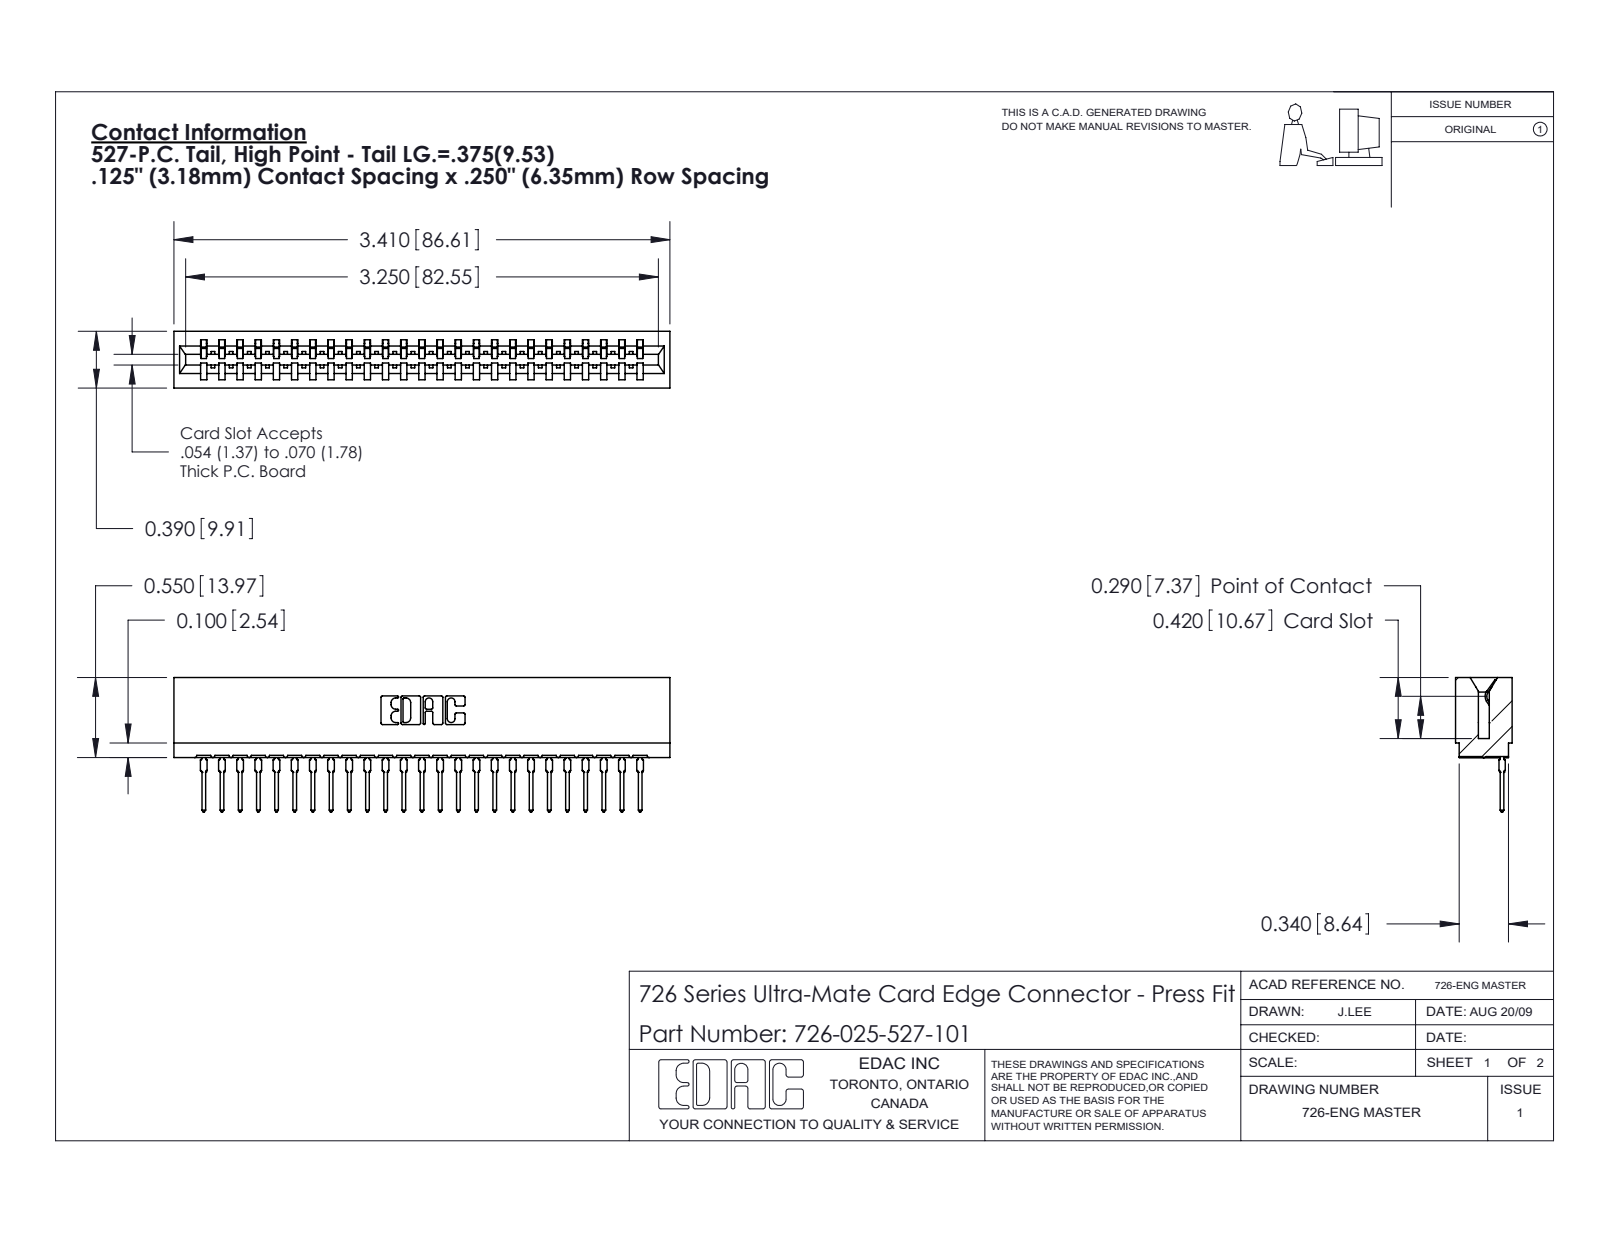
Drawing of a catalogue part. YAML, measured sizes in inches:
part_name: "746-292-001_527; 726-025-527-101; 726 Part_.515 Slot Depth - 01"
step_written_by: "SolidWorks 2020 (CONFIG_CONTROL_DESIGN)"
units: inches
bodies: {solids: 26, faces: 2797, planar: 1630, cylindrical: 517, other: 650}
overall_size: [3.41, 0.924, 0.39]
volume: 0.479
surface_area: 18.41
partial_cylinders:
  - {radius: 0.021, count: 50}
  - {radius: 0.015, count: 26}
  - {radius: 0.01, count: 22}
  - {radius: 0.007, count: 6}
  - {radius: 0.031, count: 6}
  - {radius: 0.005, count: 4}
  - {radius: 0.011, count: 4}
  - {radius: 0.026, count: 3}
face_to_face_distances: [0.057, 0.333, 0.39, 0.25, 0.025, 0.307, 0.75, 0.5, 0.083, 0.275]
